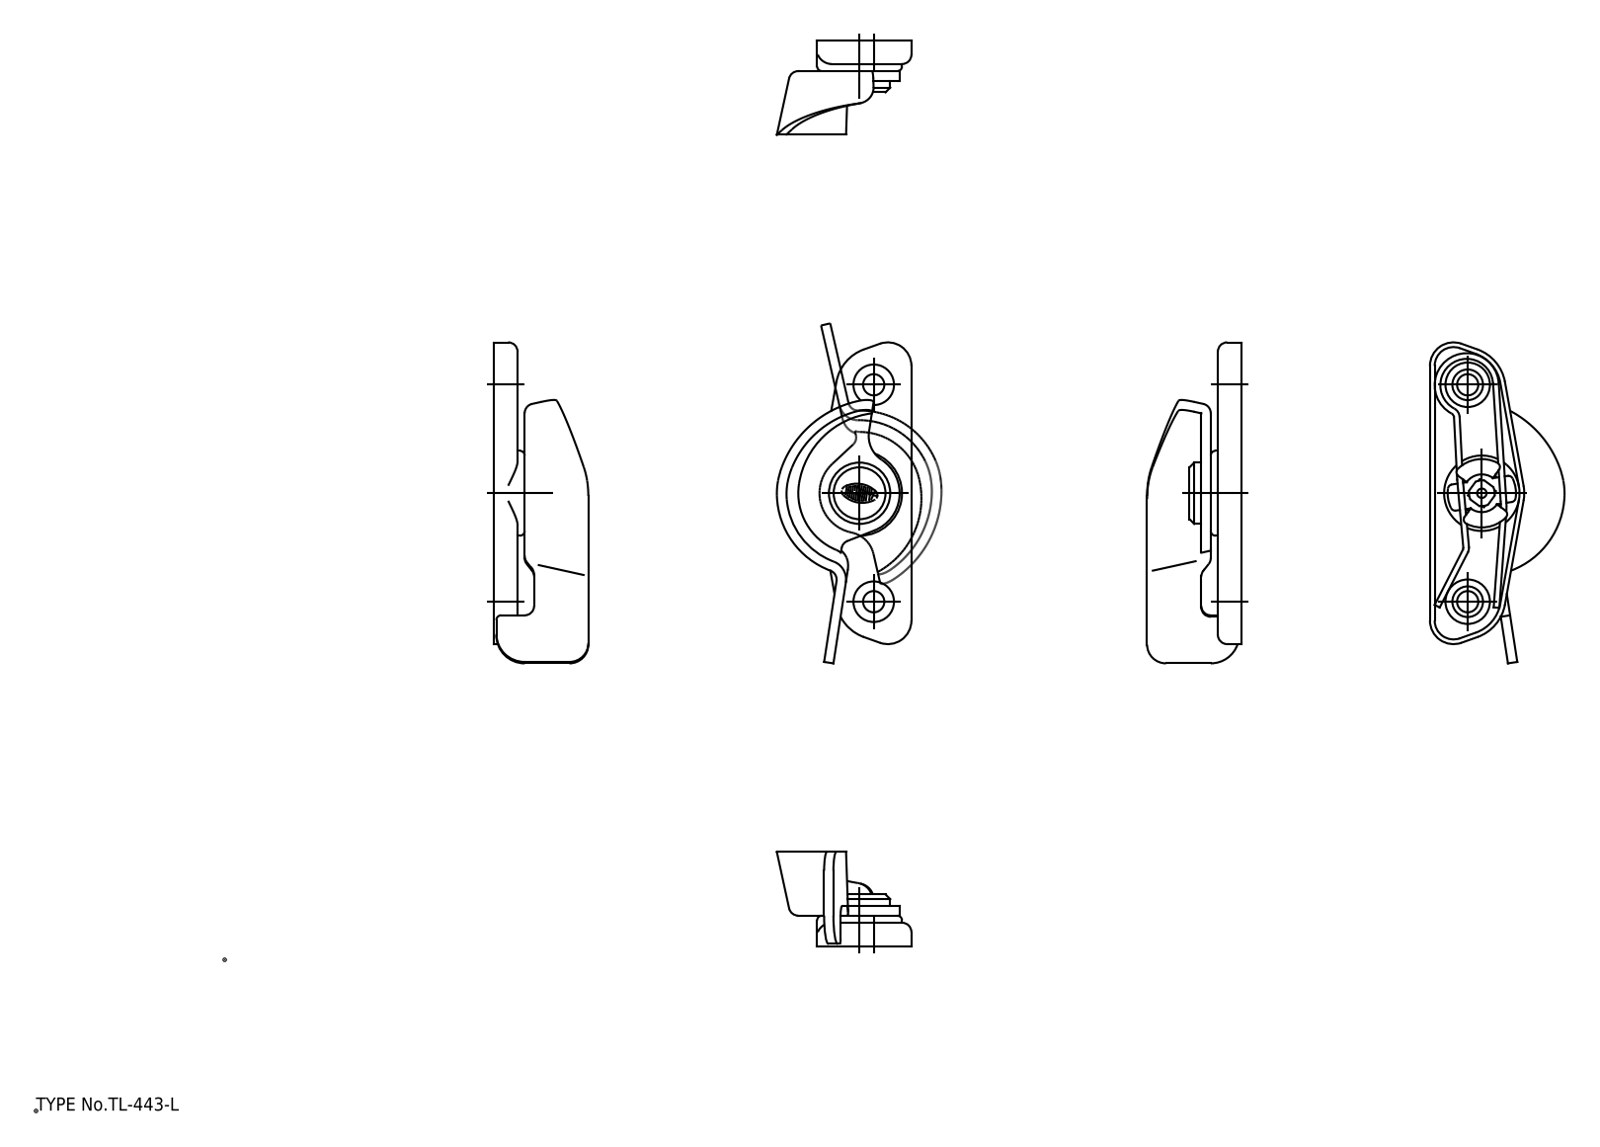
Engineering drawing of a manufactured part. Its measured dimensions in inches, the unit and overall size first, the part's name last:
Units: inches
Overall size (bounding box): 2.68 × 1.124 × 0.787
Round holes (diameter × count): ⌀0.366 ×1, ⌀0.63 ×1
Round bosses / shafts (diameter × count): ⌀0.047 ×5, ⌀0.709 ×1, ⌀0.512 ×1
Partial cylindrical surfaces — rounded edges, fillets, slot ends (radius × count): R0.039 ×14, R0.079 ×7, R0.157 ×4, R0.197 ×3, R0.236 ×2, R0.315 ×2, R0.354 ×2, R0.138 ×1
Main face-to-face distances: 0.039, 0.059, 0.079, 0.098, 0.177, 0.138, 0.197, 0.217, 0.157, 0.02
Volume: 0.29 in³ · Surface area: 10.93 in²
Bodies: 3 solids, 183 faces (60 planar, 61 cylindrical, 62 other)
Part name (STEP PRODUCT): レバー; ベース; スプリング
STEP written by: spGate 19.8.4 (****-****-****-****) (AUTOMOTIVE_DESIGN)
